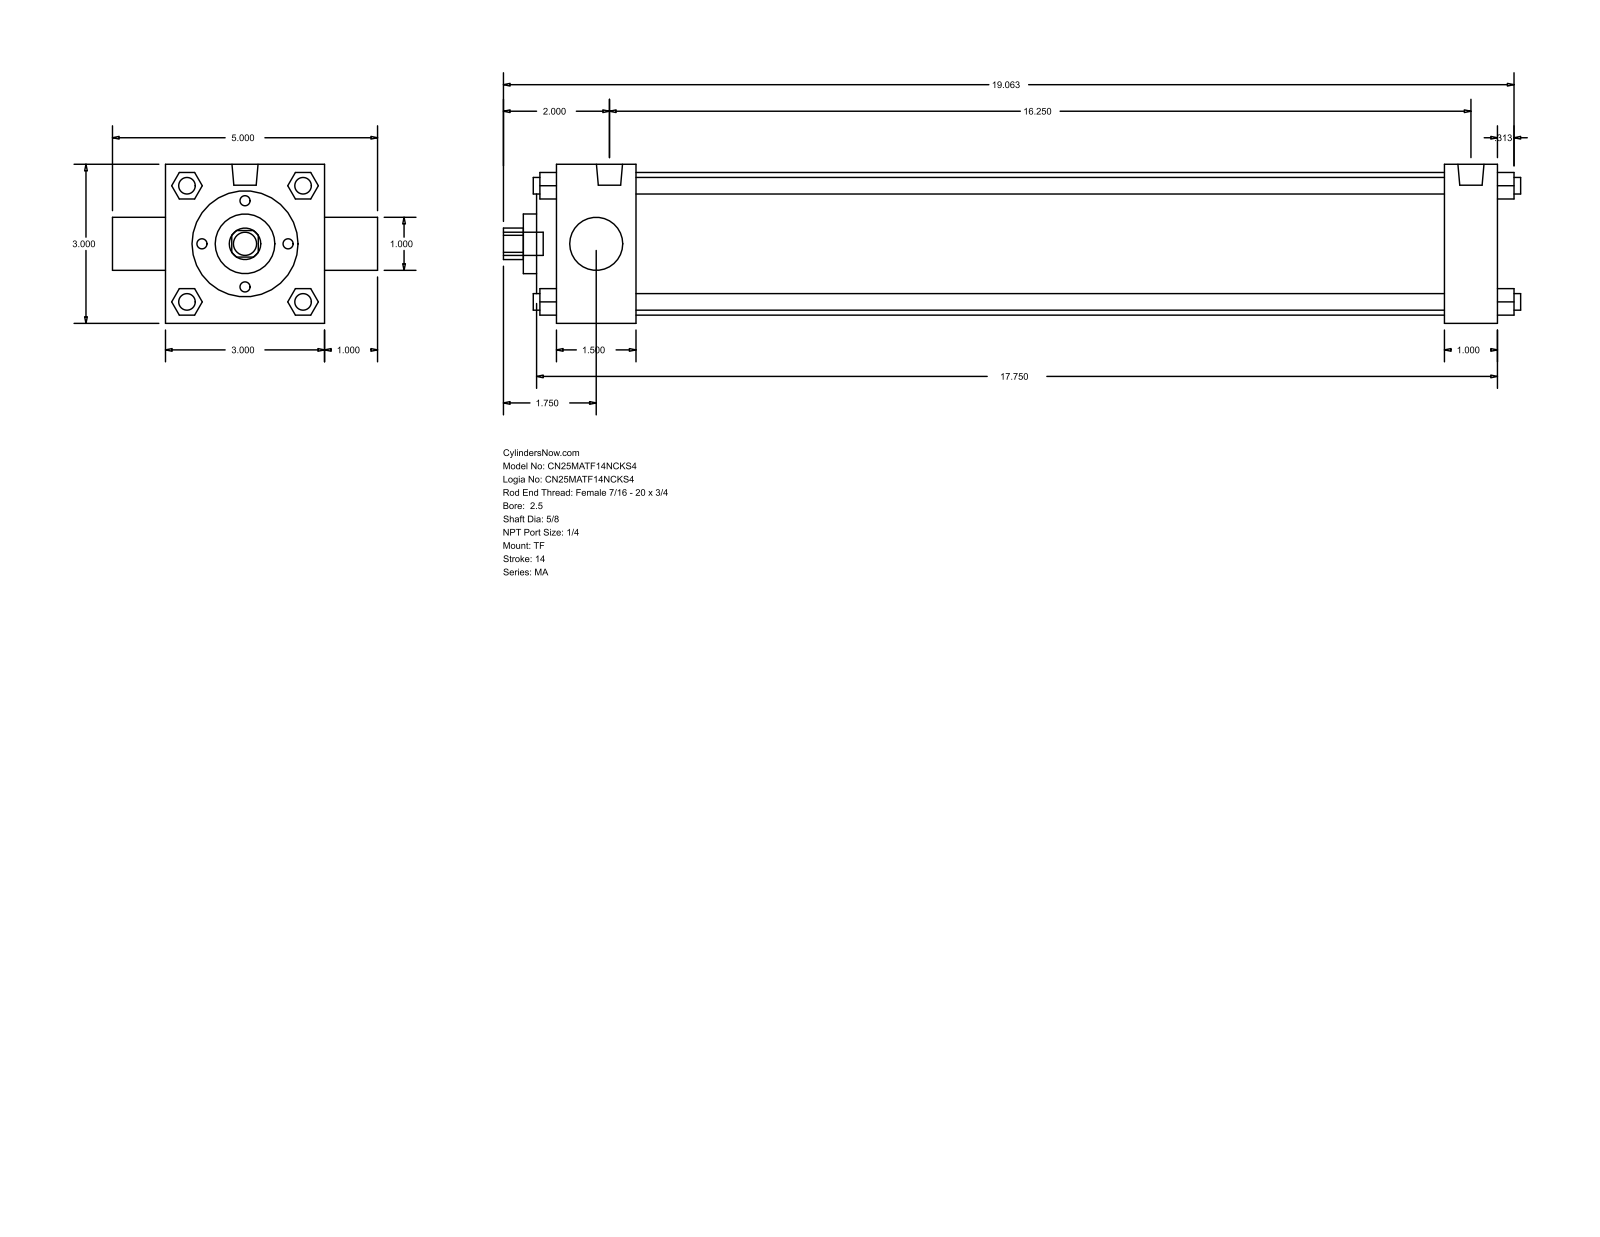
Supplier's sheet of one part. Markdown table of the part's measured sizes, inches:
| quantity | value |
| --- | --- |
| part name | MA_TF__0250_0.625 |
| STEP written by | GSSL Pune (CONFIG_CONTROL_DESIGN) |
| units | inches |
| bodies | 0 solids, 122 faces (93 planar, 29 cylindrical, 0 other) |
| overall size | 19.187 × 5 × 3 |
| round holes (diameter × count) | 0.625 × 1, 1 × 1, 1.125 × 1, 2 × 1, 2.69 × 1 |
| round bosses / shafts (diameter × count) | 0.313 × 7, 0.492 × 2, 0.437 × 1 |
| partial cylindrical surfaces (radius × count) | 0.297 × 1 |
| main face-to-face distances | 3, 17.75, 1, 1.5, 16.75, 15.25, 16.25, 0.5, 0.375, 1.875 |
